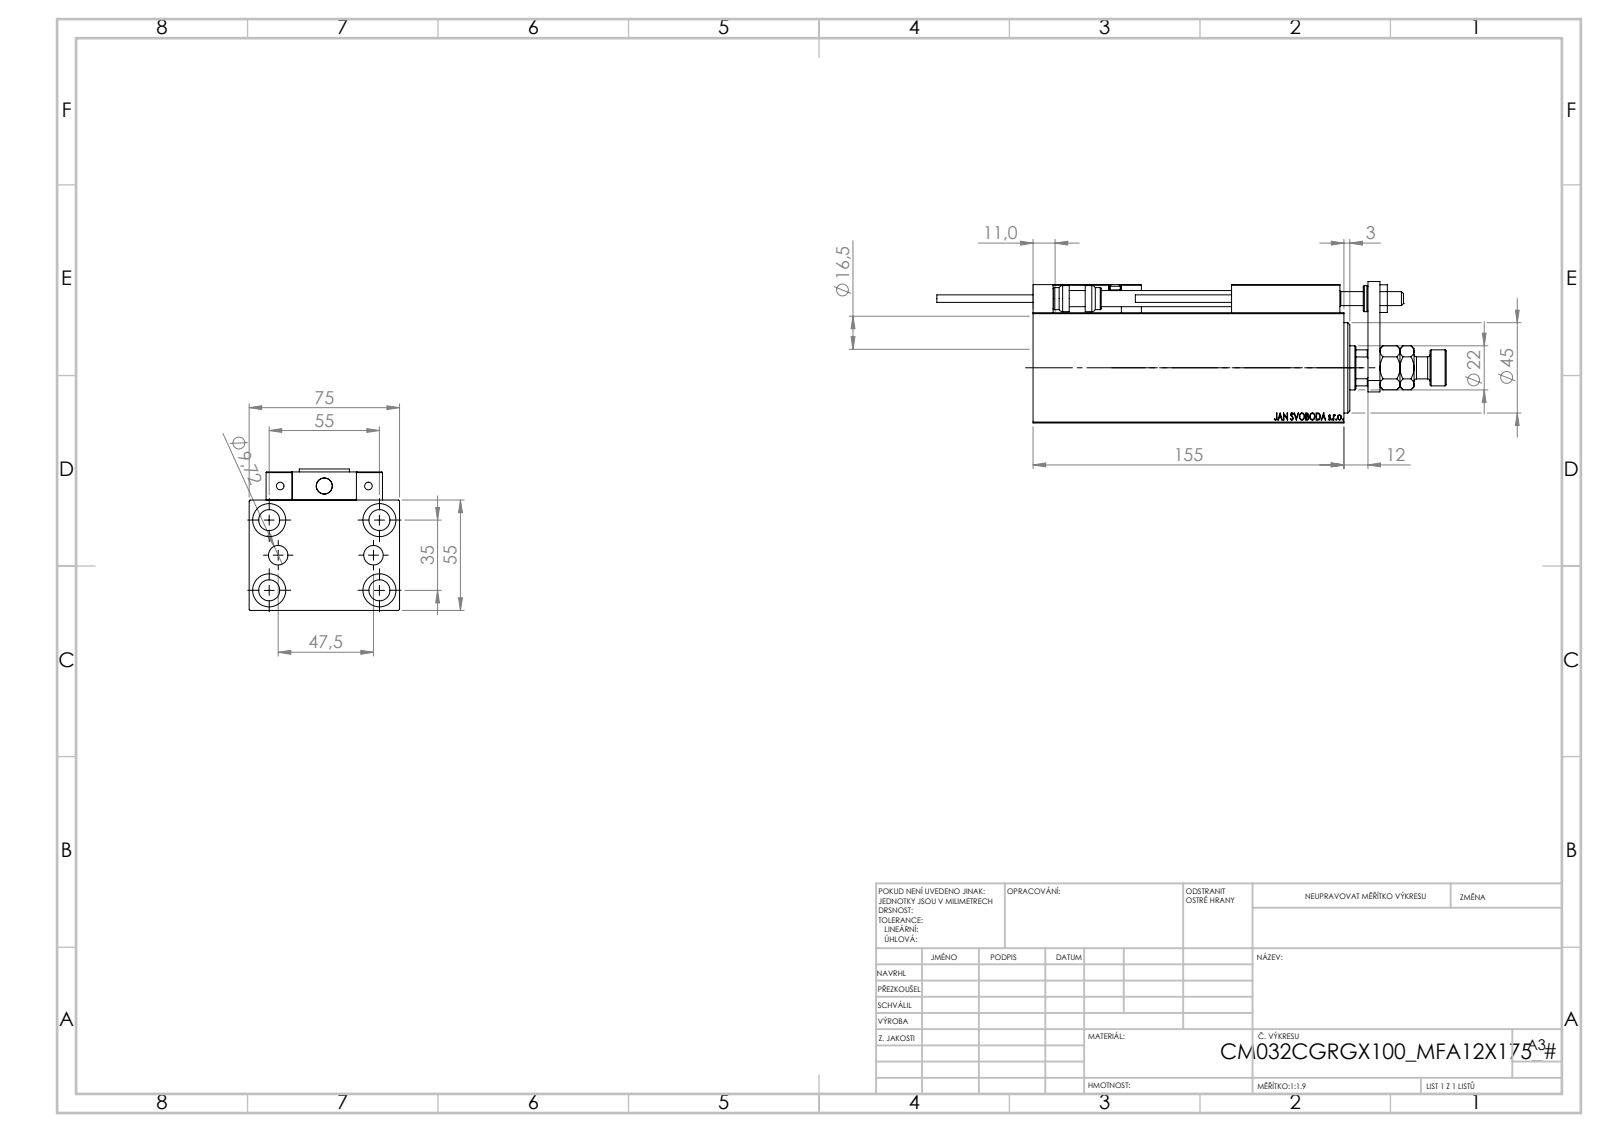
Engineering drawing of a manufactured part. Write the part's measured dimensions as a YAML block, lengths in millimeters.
part_name: "ZARAZKA; SWITCH X; X_Y_MFA; TYC_L79 (+7 more)"
step_written_by: "SolidWorks 2019 (CONFIG_CONTROL_DESIGN)"
units: millimeters
bodies: {solids: 24, faces: 1330, planar: 576, cylindrical: 188, other: 566}
overall_size: [254, 75, 70.5]
volume: 592403
surface_area: 132848
round_holes:
  - {diameter: 4, count: 6}
  - {diameter: 8, count: 5}
  - {diameter: 10.5, count: 5}
  - {diameter: 16.5, count: 5}
  - {diameter: 3.2, count: 4}
  - {diameter: 5, count: 2}
  - {diameter: 9.72, count: 2}
  - {diameter: 7, count: 1}
  - {diameter: 22, count: 1}
  - {diameter: 25.5, count: 1}
  - {diameter: 32, count: 1}
  - {diameter: 34, count: 1}
round_bosses_or_shafts:
  - {diameter: 11, count: 2}
  - {diameter: 5, count: 2}
  - {diameter: 3.8, count: 2}
  - {diameter: 18, count: 1}
  - {diameter: 13, count: 1}
partial_cylinders:
  - {radius: 0.3, count: 30}
  - {radius: 3, count: 2}
  - {radius: 10.5, count: 1}
face_to_face_distances: [55, 75, 14, 5, 3, 69, 23, 45, 18, 10]
hole_center_spacings: [17.9, 32.6, 54.16, 11.37, 20, 23.75, 29.59, 29.69]
